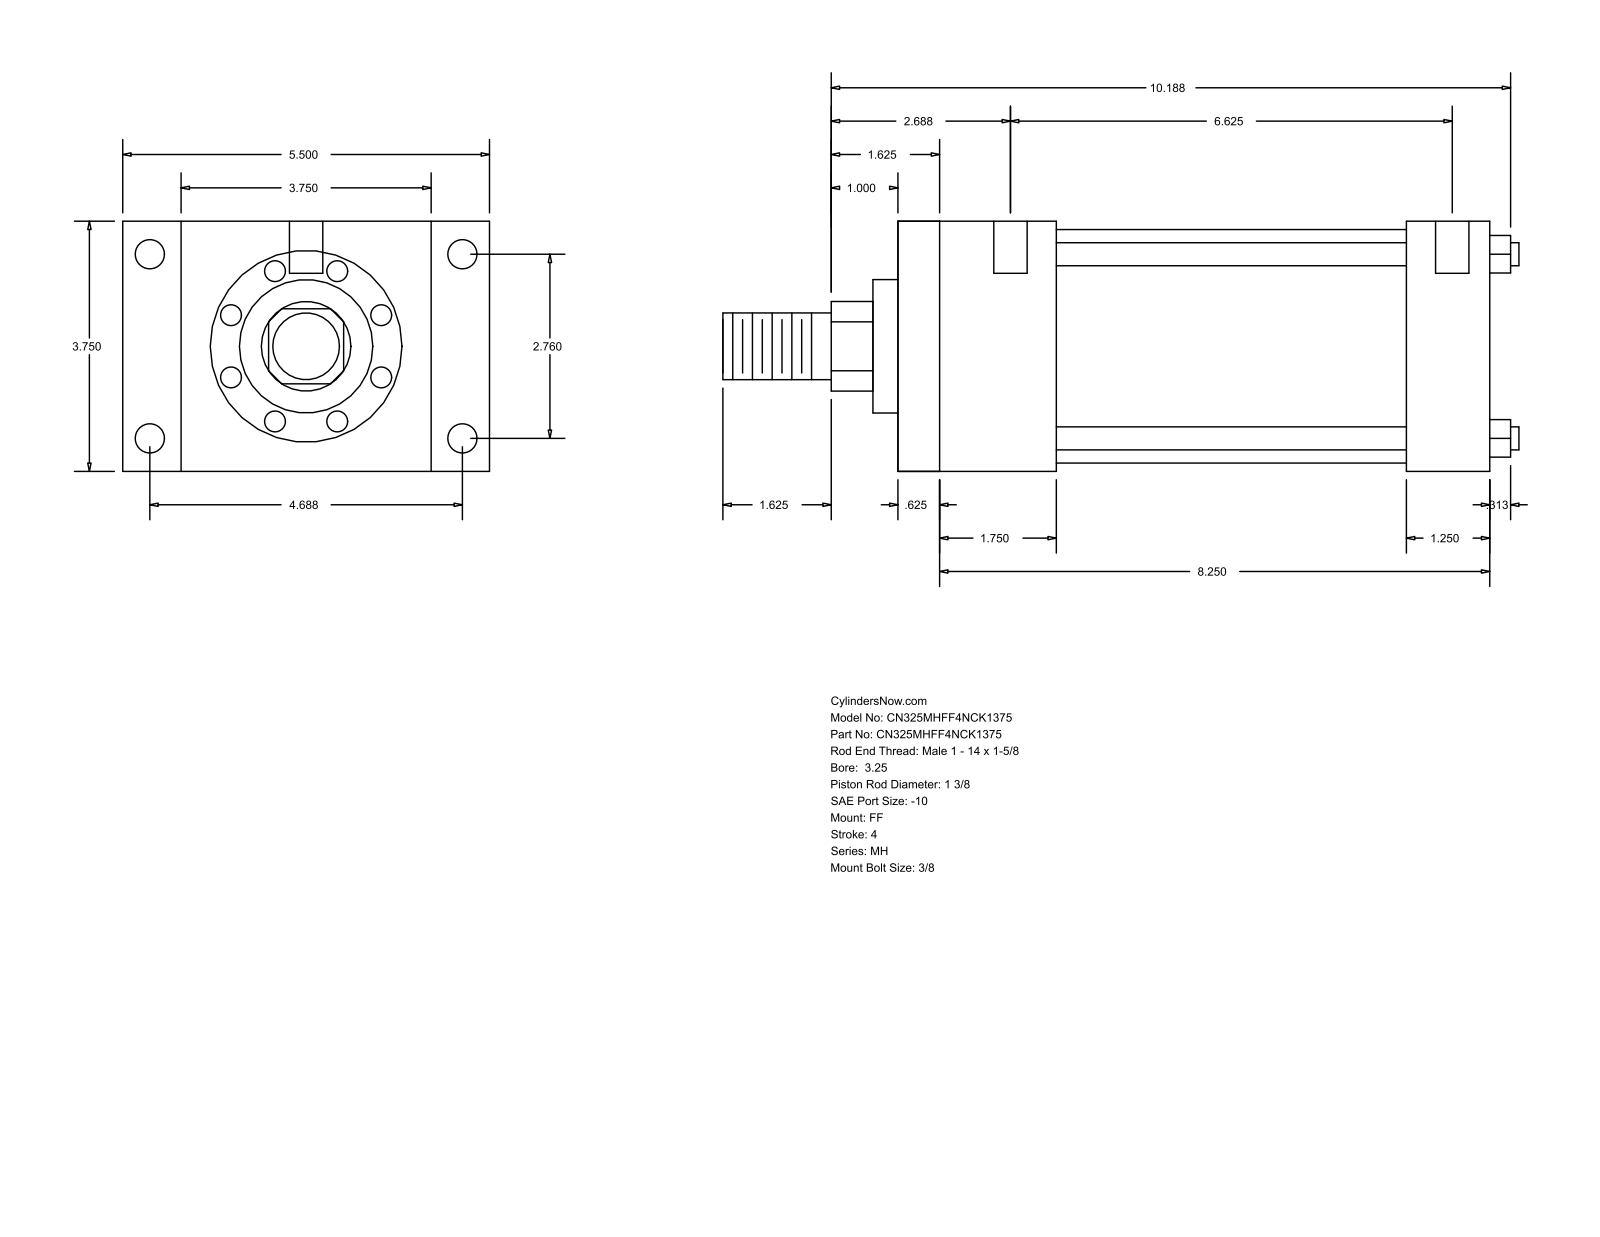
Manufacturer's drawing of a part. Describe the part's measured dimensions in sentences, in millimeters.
The part is named "MH_FF__0325_1.375". Its 3-D file was written by "GSSL Pune (CONFIG_CONTROL_DESIGN)". It is 0 solids with 92 faces: 64 planar, 28 cylindrical and 0 other. Overall it measures 303.21 by 139.7 by 95.25 millimeters. Round holes: 4 of diameter 5.56, 4 of diameter 11.13, 2 of diameter 12.7. Round bosses or shafts: 4 of diameter 8.76, 1 of diameter 88.9, 1 of diameter 50.8, 1 of diameter 34.92, 1 of diameter 25.4. Partial cylindrical surfaces (rounded edges, fillets, slot ends): 1 of radius 17.06. The main face-to-face distances are 95.24, 225.42, 15.87, 209.55, 22.23, 117.47, 193.67, 177.8, 31.75, 60.32. The hole center spacings are 70.1, 119.06, 138.16, 174.63, 1.59, 4.76, 168.28, 169.87.
